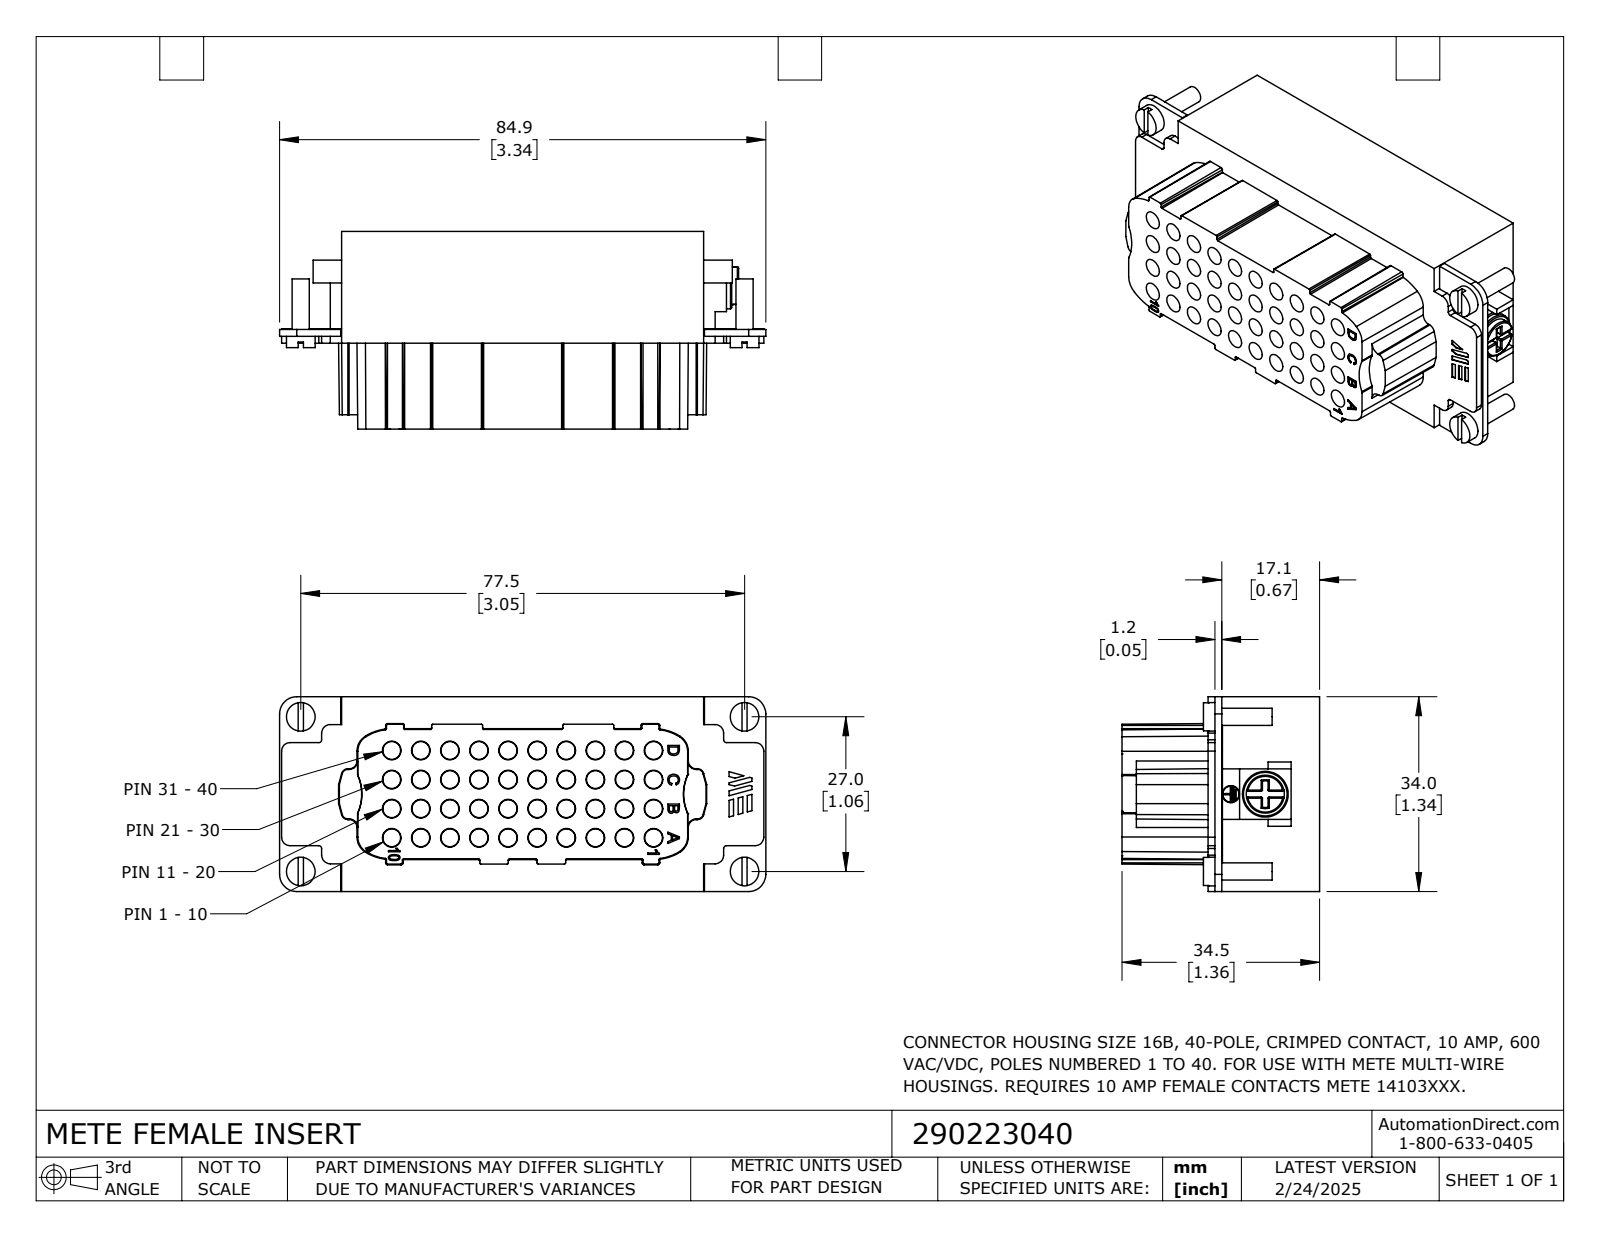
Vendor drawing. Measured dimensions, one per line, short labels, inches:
name: 290223040
written by: SolidWorks 2024 (CONFIG_CONTROL_DESIGN)
unit: in
bodies: 1 solid, 485 faces (247 planar, 87 cylindrical, 151 other)
size: 3.343 × 1.358 × 1.339
volume: 3.298 in³; area: 40.64 in²
holes: 1× ⌀0.118
bosses: 4× ⌀0.197, 4× ⌀0.118, 1× ⌀0.315, 1× ⌀0.261, 1× ⌀0.11
rounds: 28× R0.008, 8× R0.059, 4× R0.02, 4× R0.118, 1× R0.091
face distances: 1.339, 0.768, 0.591, 1.358, 0.047, 2.488, 0.098, 0.189, 1.15, 0.689
